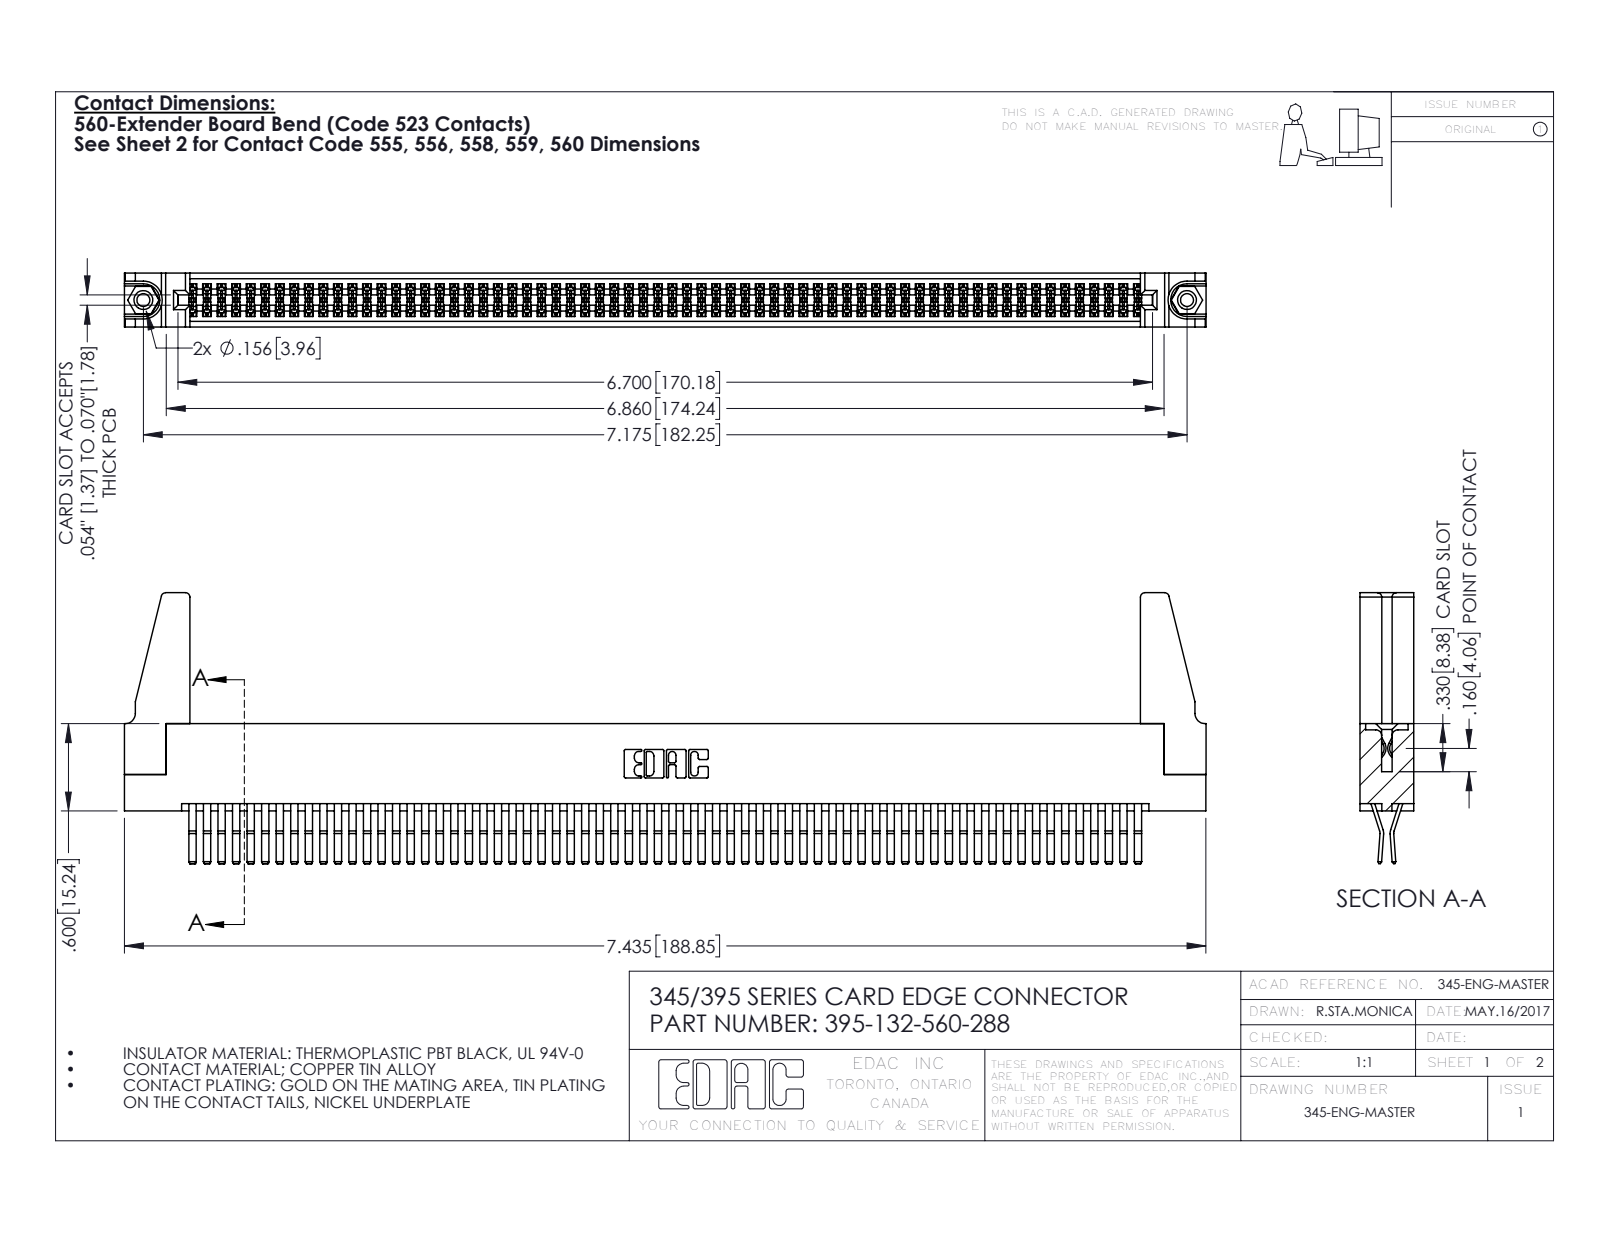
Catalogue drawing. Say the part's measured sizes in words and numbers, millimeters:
The part is named "345-220-078_345-220-088; 345 Part_Flush Mounting Lugs - 0.156 Dia-TH; 345-292-001_560 Tail; 395-132-560-288 (+1 more)". Its 3-D file was written by "SolidWorks 2016 (CONFIG_CONTROL_DESIGN)". It is 137 solids with 7114 faces: 4508 planar, 2590 cylindrical and 16 other. Overall it measures 188.9 by 47.3 by 9.4 millimeters. Its volume is 22 680 cubic millimeters and its surface area 34 540 square millimeters. Round holes: 2 of diameter 2.3, 2 of diameter 3.2, 2 of diameter 4, 1 of diameter 1.6. Round bosses or shafts: 2 of diameter 3.9. Partial cylindrical surfaces (rounded edges, fillets, slot ends): 199 of radius 0.2, 22 of radius 0.3, 8 of radius 0.8, 6 of radius 0.2, 6 of radius 0.8, 3 of radius 0.7, 2 of radius 0.3, 2 of radius 0.4. The main face-to-face distances are 1.8, 7.6, 0.6, 9.4, 5.1, 2.5, 6.9, 5.7, 4.4, 3.8. The hole center spacings are 6.9, 176.3, 182.2.
